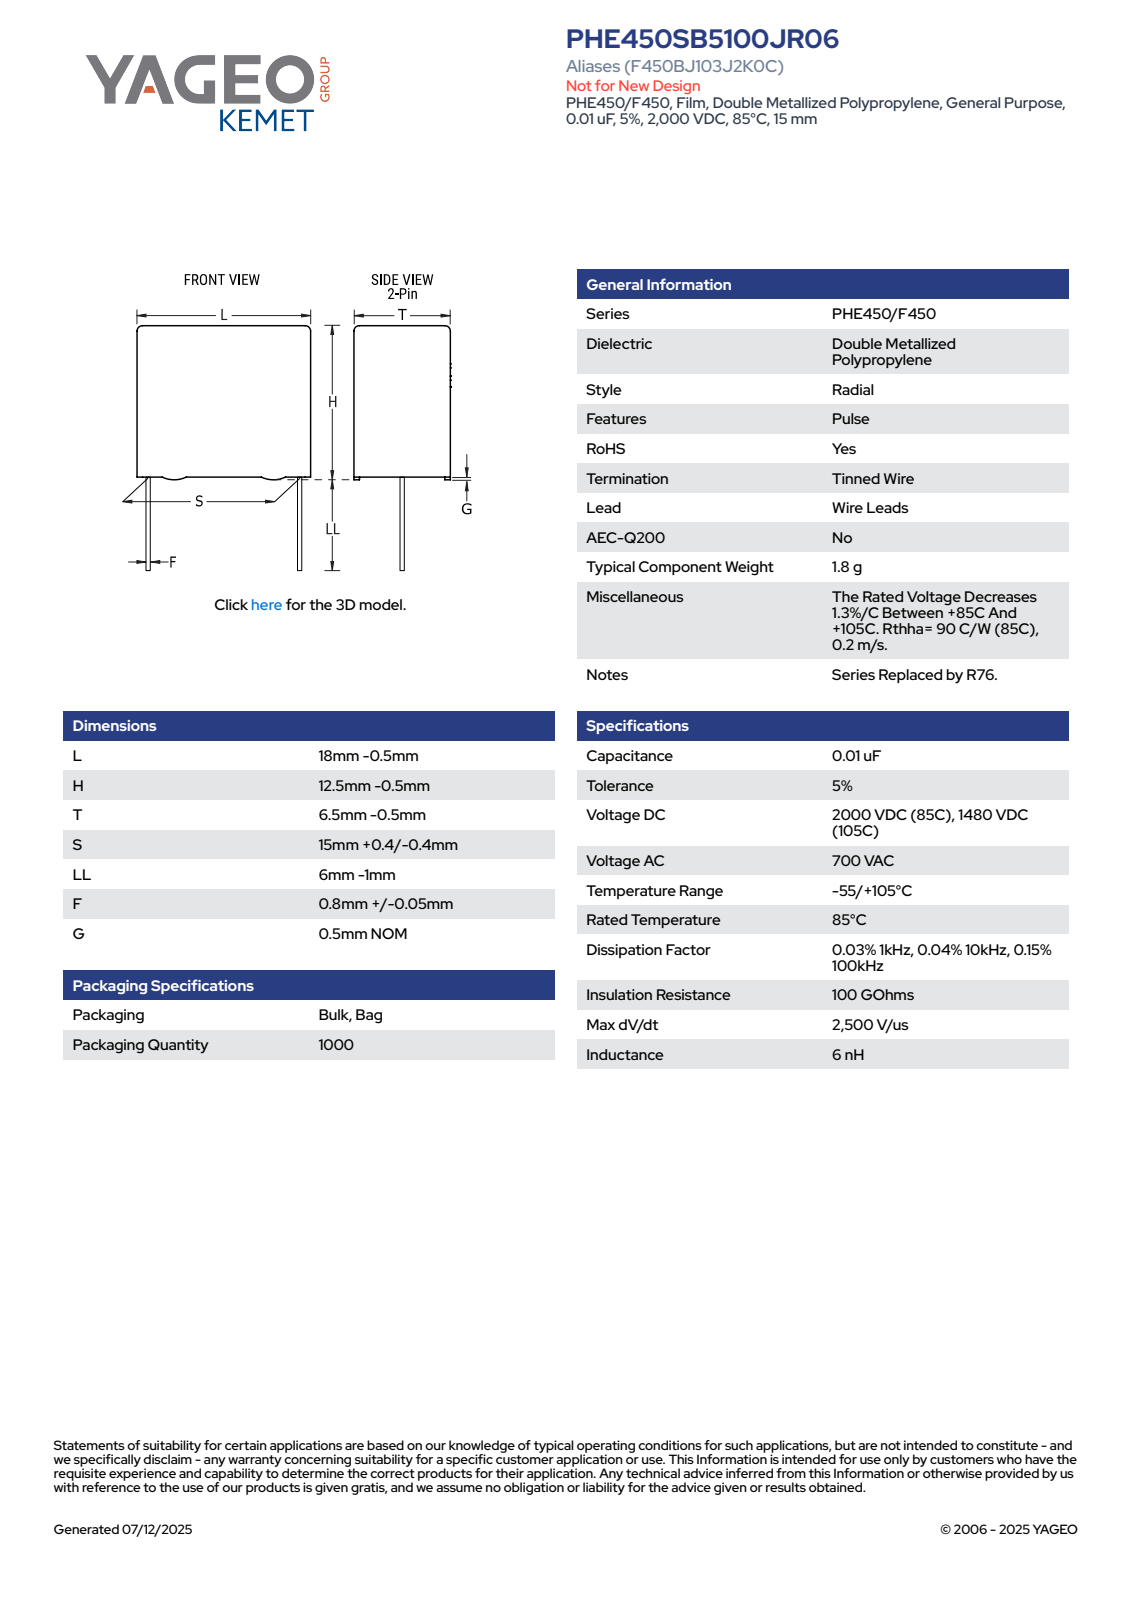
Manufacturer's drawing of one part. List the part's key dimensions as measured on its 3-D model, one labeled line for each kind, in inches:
Part name (STEP PRODUCT): CFR_RBG_18X12.5X6.5_L17.5H12T6S15LL5F0.85G0.5
STEP written by: SolidWorks 2021 (AUTOMOTIVE_DESIGN)
Units: inches
Bodies: 4 solids, 89 faces (81 planar, 8 cylindrical, 0 other)
Overall size (bounding box): 0.689 × 0.669 × 0.236
Volume: 0.074 in³ · Surface area: 1.26 in²
Round bosses / shafts (diameter × count): ⌀0.033 ×2
Partial cylindrical surfaces — rounded edges, fillets, slot ends (radius × count): R0.02 ×4
Main face-to-face distances: 0.236, 0.453, 0.689, 0.013, 0.223, 0.02, 0.472, 0.209, 0.197, 0.217
